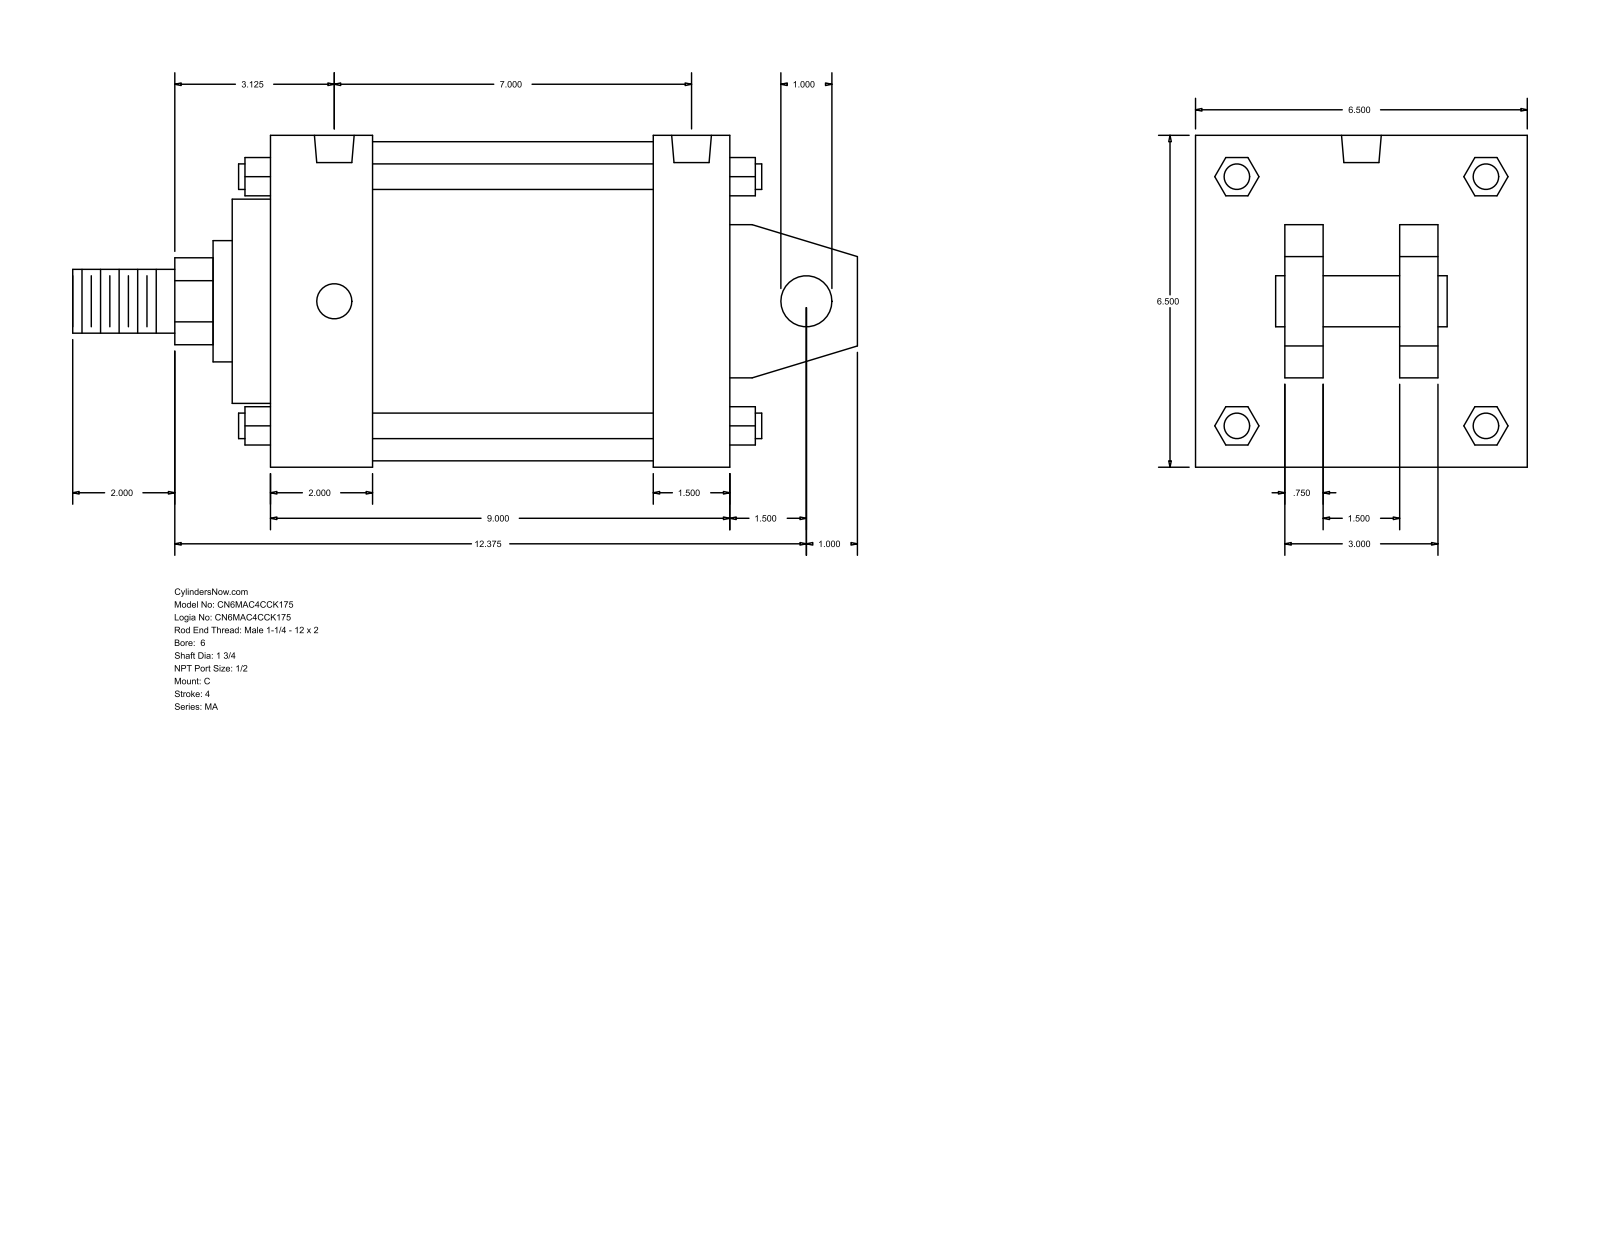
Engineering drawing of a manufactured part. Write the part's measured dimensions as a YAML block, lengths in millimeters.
part_name: "MA_C__0600_1.75"
step_written_by: "GSSL Pune (CONFIG_CONTROL_DESIGN)"
units: millimeters
bodies: {solids: 0, faces: 141, planar: 109, cylindrical: 32, other: 0}
overall_size: [390.52, 165.1, 165.1]
round_holes:
  - {diameter: 17.46, count: 4}
  - {diameter: 19.77, count: 2}
round_bosses_or_shafts:
  - {diameter: 12.7, count: 4}
  - {diameter: 158.75, count: 1}
  - {diameter: 101.6, count: 1}
  - {diameter: 60.33, count: 1}
  - {diameter: 44.45, count: 1}
  - {diameter: 31.75, count: 1}
  - {diameter: 25.4, count: 1}
partial_cylinders:
  - {radius: 21.63, count: 1}
face_to_face_distances: [165.1, 228.61, 19.05, 63.5, 101.6, 50.8, 44.45, 120.65, 57.15, 177.81]
hole_center_spacings: [177.8]
